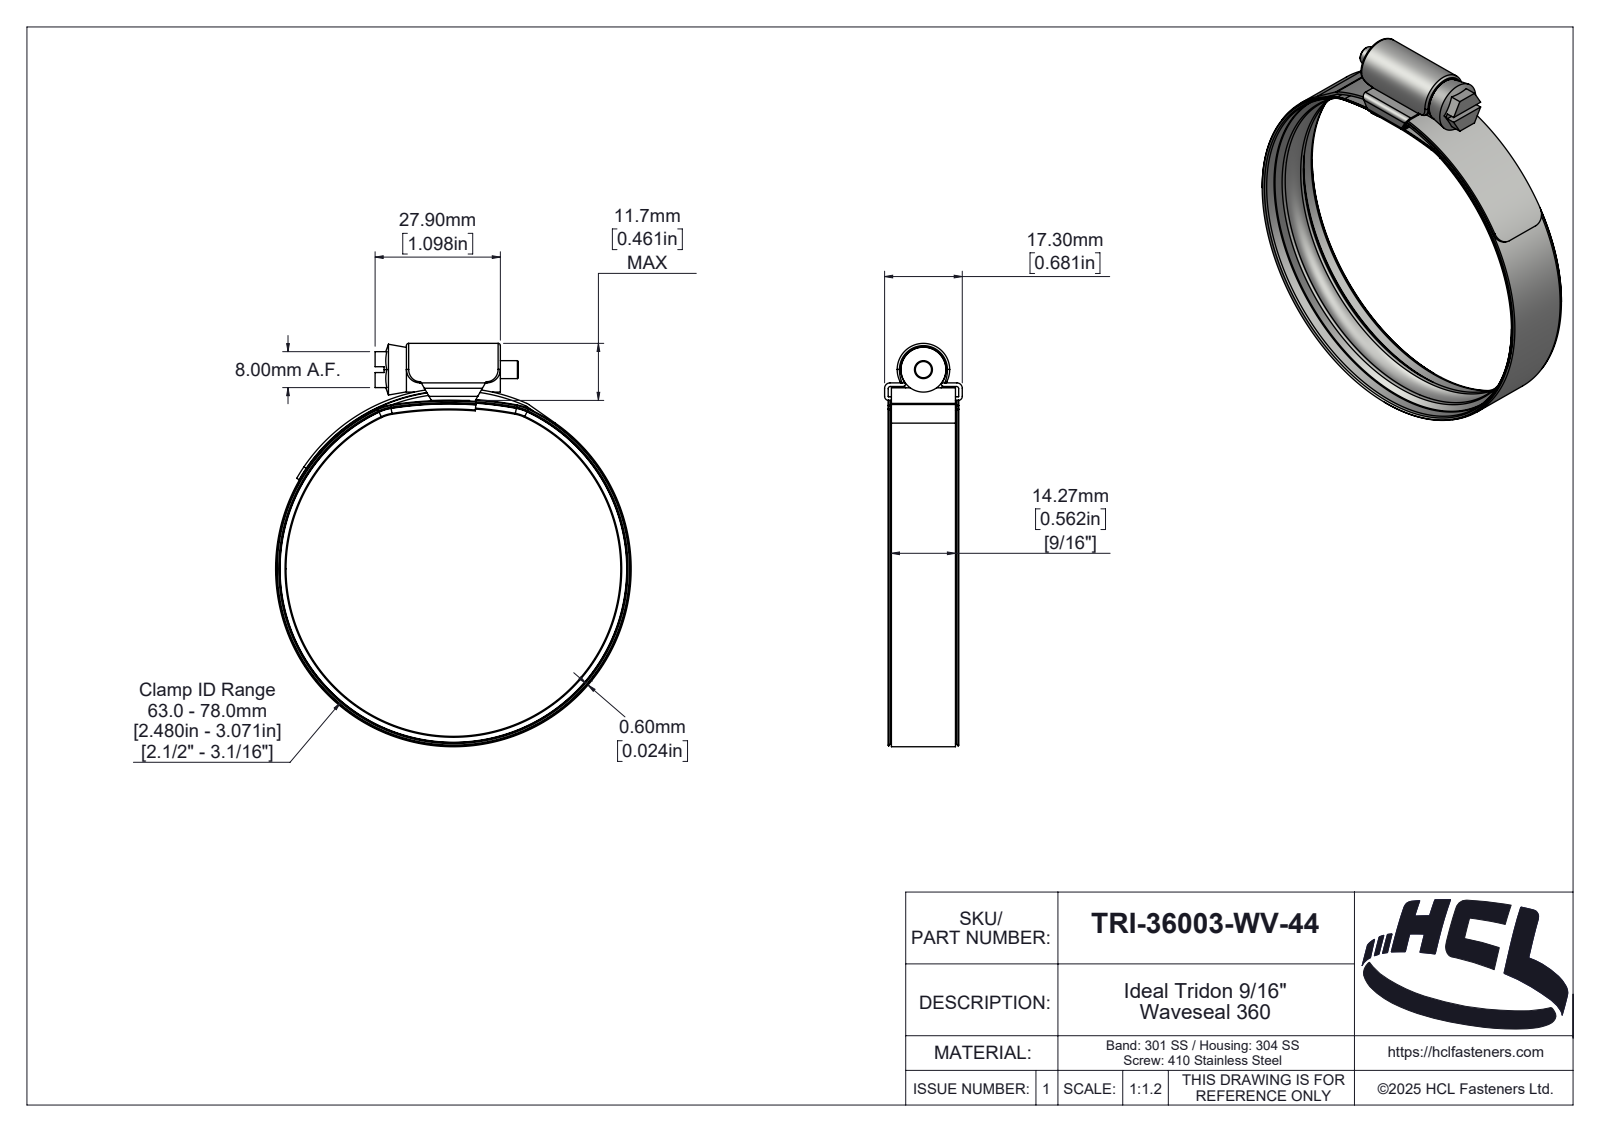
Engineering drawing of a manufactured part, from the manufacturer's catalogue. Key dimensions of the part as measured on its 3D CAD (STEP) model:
Part name (STEP PRODUCT): TRI-36003-WV-44
STEP written by: SolidWorks 2025 (AUTOMOTIVE_DESIGN)
Units: millimetres
Bodies: 4 solids, 418 faces (42 planar, 119 cylindrical, 257 other)
Overall size (bounding box): 89.8 × 79.2 × 17.3
Volume: 6 209 mm³ · Surface area: 20 360 mm²
Round holes (diameter × count): ⌀77.4 ×1, ⌀78 ×1
Round bosses / shafts (diameter × count): ⌀79.2 ×1, ⌀77.8 ×1, ⌀10 ×1, ⌀4 ×1
Partial cylindrical surfaces — rounded edges, fillets, slot ends (radius × count): R0.5 ×6, R3 ×4, R0.1 ×2, R0.9 ×2, R1.2 ×2, R9.9 ×2, R10.1 ×2, R0.46 ×1
Main face-to-face distances: 0.8, 14.26, 3.1, 0.6, 2.3, 3.9, 27.9, 1.52, 15.78, 16.5
